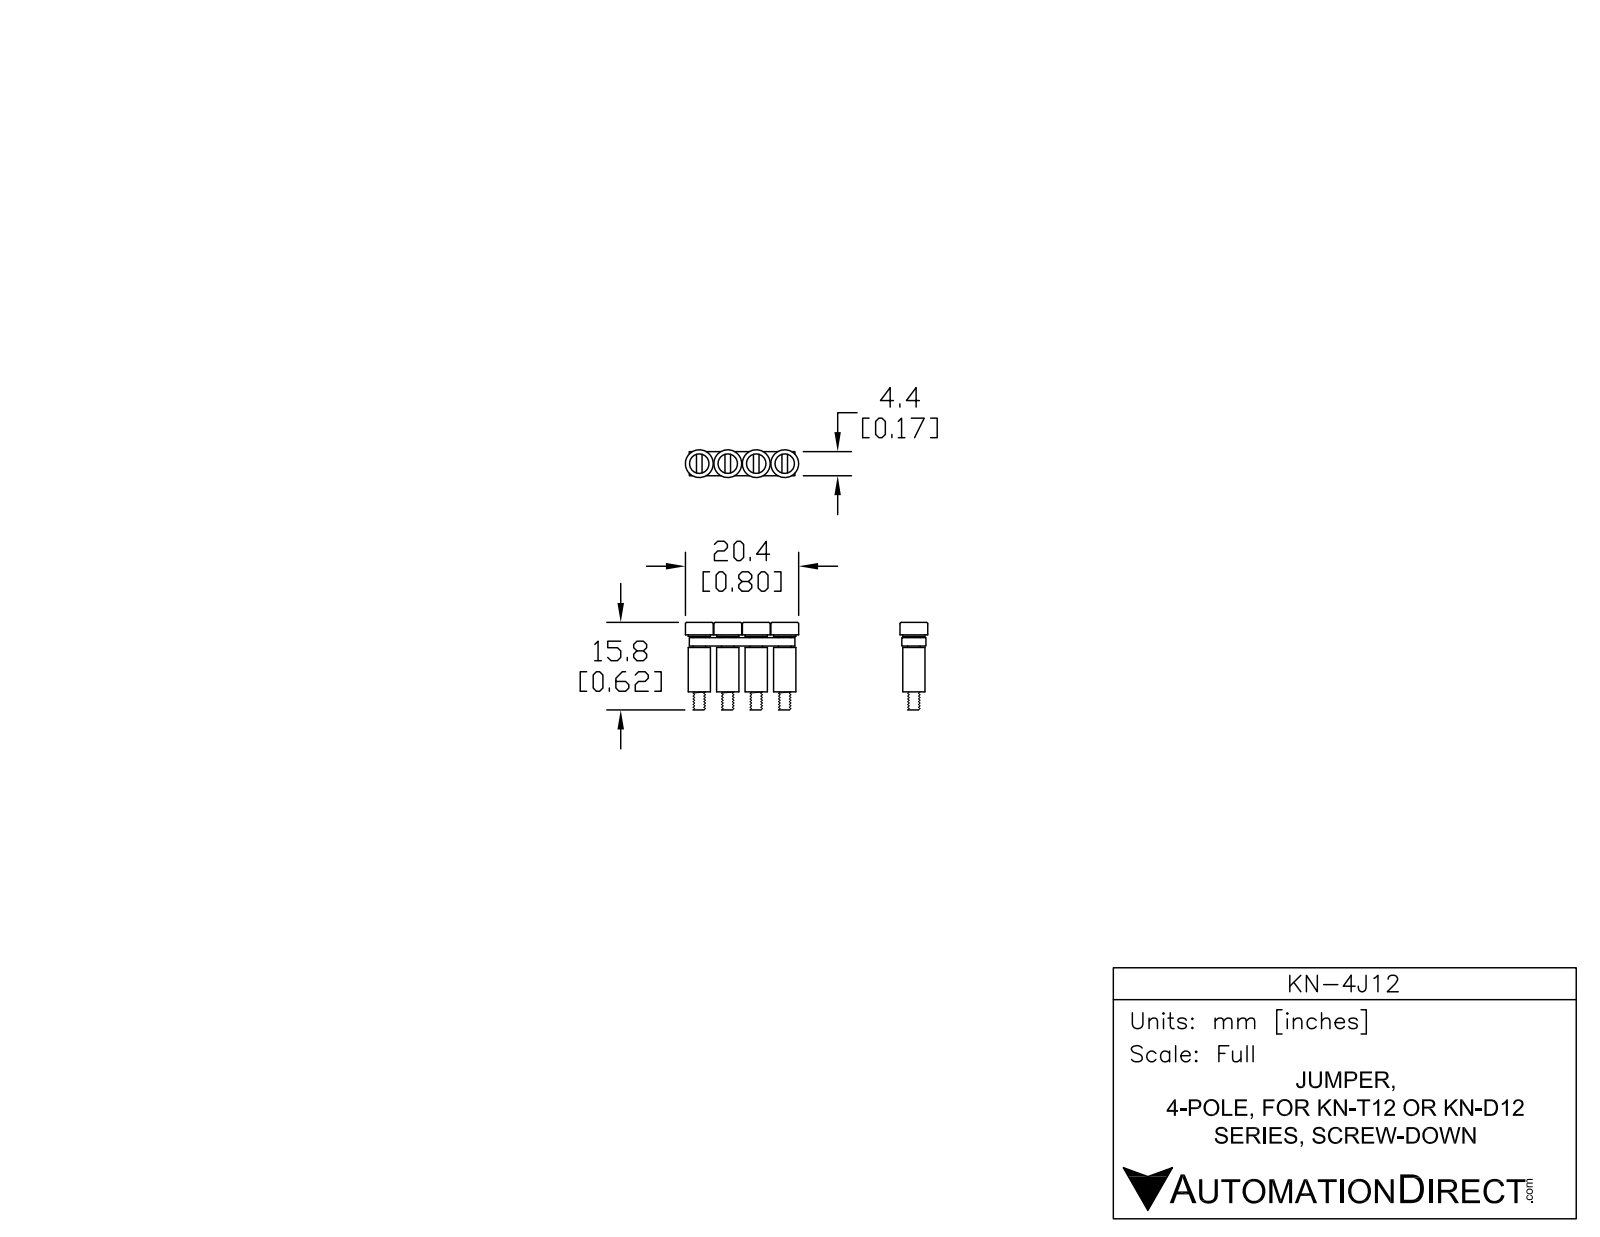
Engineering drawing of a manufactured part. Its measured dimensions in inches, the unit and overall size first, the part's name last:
Units: inches
Overall size (bounding box): 0.802 × 0.62 × 0.197
Round holes (diameter × count): ⌀0.118 ×4, ⌀0.138 ×4
Round bosses / shafts (diameter × count): ⌀0.197 ×4, ⌀0.157 ×4, ⌀0.089 ×4
Main face-to-face distances: 0.059, 0.079, 0.069, 0.089, 0.02, 0.039, 0.108, 0.148, 0.404, 0.171
Hole centre spacings: 0.202, 0.202, 0.404, 0.404, 0.606
Volume: 0.041 in³ · Surface area: 2.984 in²
Bodies: 13 solids, 134 faces (58 planar, 52 cylindrical, 24 other)
Part name (STEP PRODUCT): KN-4J12
STEP written by: SolidWorks 2014 (AUTOMOTIVE_DESIGN)
